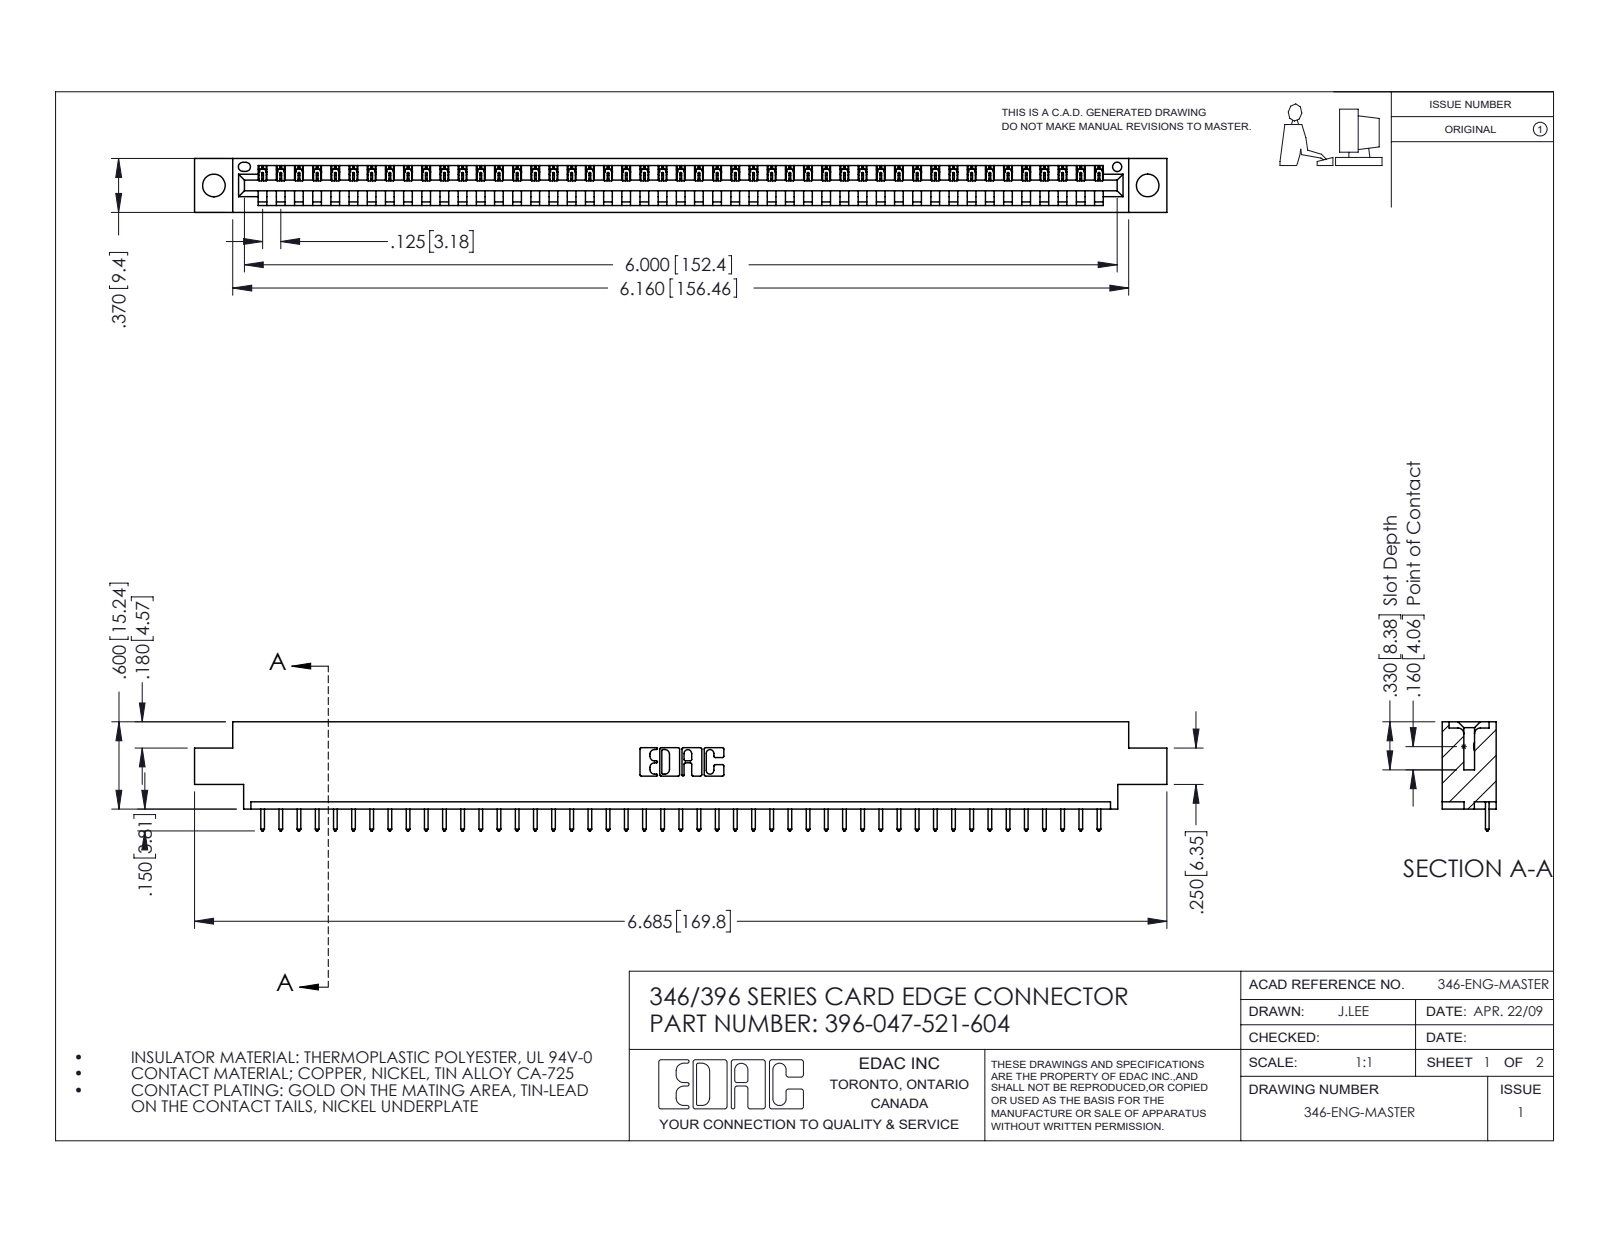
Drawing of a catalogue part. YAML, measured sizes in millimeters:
part_name: "346 Part_0.170 Offset - 0.156 Dia-TH; 396-047-521-604; 345-292-001_345-293-121"
step_written_by: "SolidWorks 2016 (CONFIG_CONTROL_DESIGN)"
units: millimeters
bodies: {solids: 48, faces: 2852, planar: 1960, cylindrical: 892, other: 0}
overall_size: [169.8, 19.1, 9.4]
volume: 15900
surface_area: 19370
round_holes:
  - {diameter: 4, count: 2}
  - {diameter: 1.6, count: 1}
partial_cylinders:
  - {radius: 0.2, count: 94}
  - {radius: 0.3, count: 94}
  - {radius: 0.3, count: 22}
  - {radius: 0.2, count: 6}
  - {radius: 0.8, count: 6}
  - {radius: 0.7, count: 3}
  - {radius: 0.8, count: 2}
  - {radius: 1, count: 2}
face_to_face_distances: [1.2, 8.2, 9.4, 6.4, 1.8, 7.6, 0.6, 3.8, 5.6, 2.5]
hole_center_spacings: [6.2, 157.8, 163.1]
